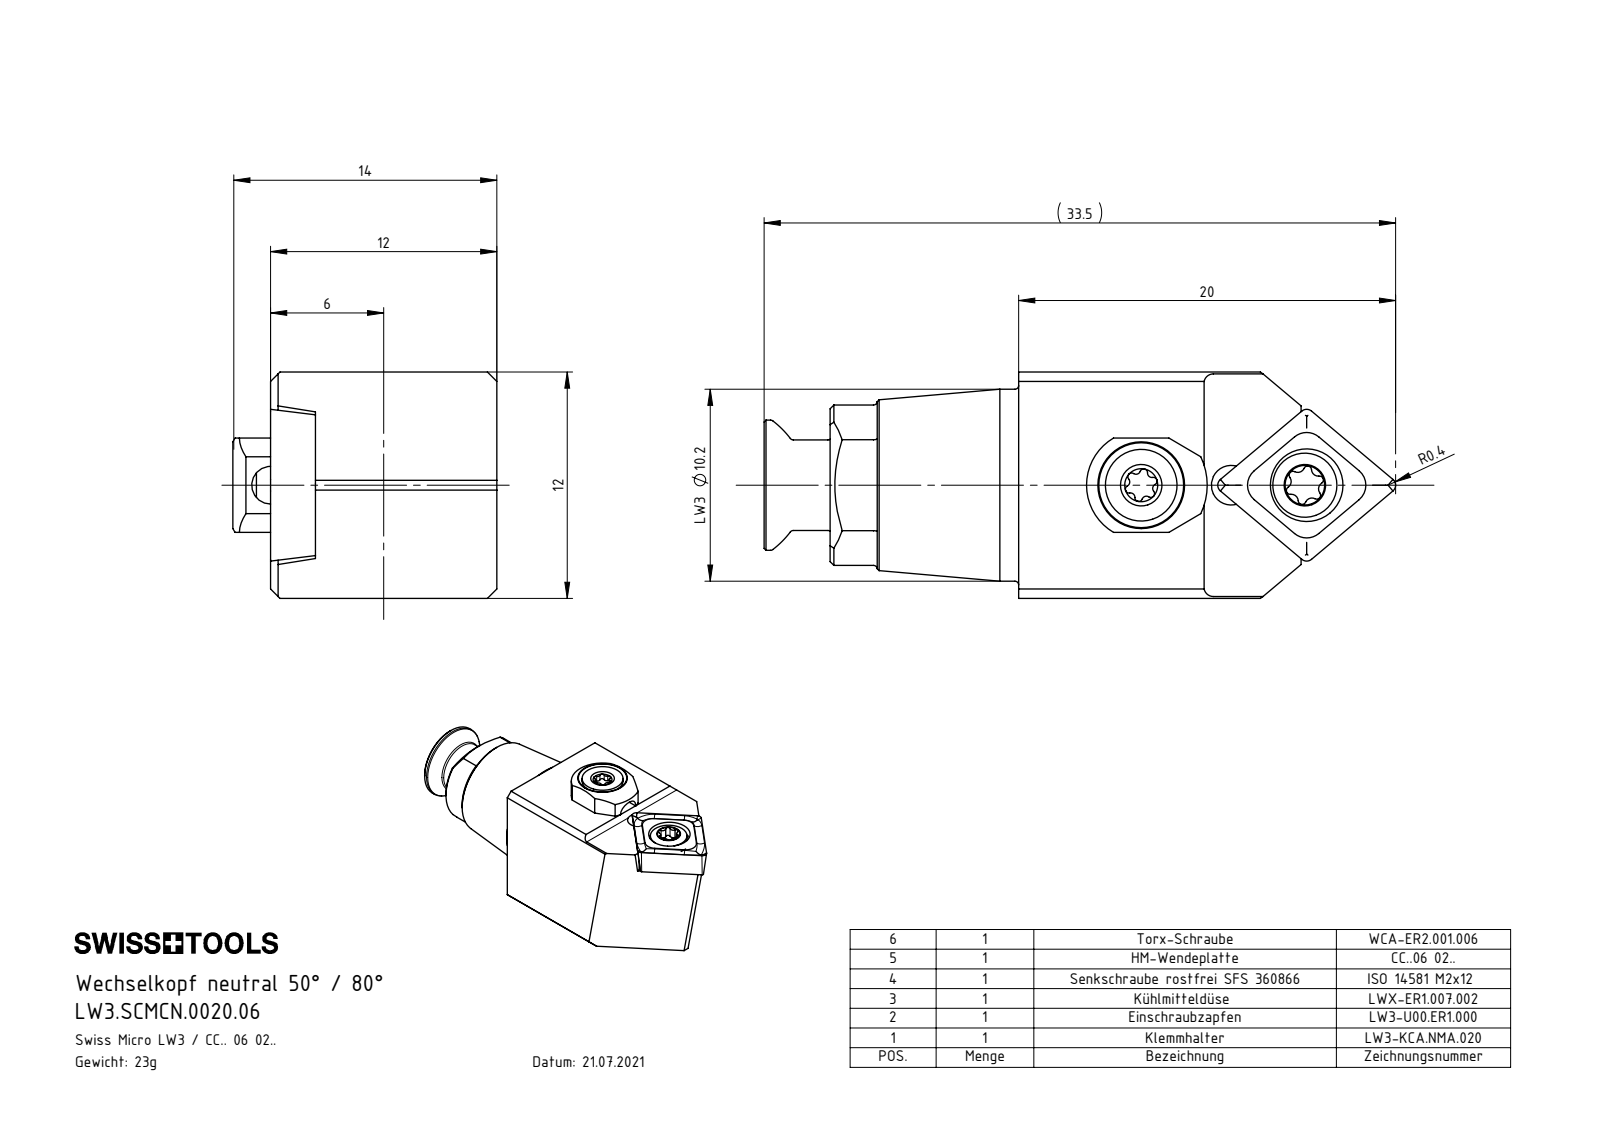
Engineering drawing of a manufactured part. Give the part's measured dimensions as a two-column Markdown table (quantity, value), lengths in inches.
| quantity | value |
| --- | --- |
| part name | LWX-ER1.007.002; ISO 14581 - M2x12; LW3-U00.ER1.000_B; CCMT060204 (+3 more) |
| STEP written by | SolidWorks 2017 (CONFIG_CONTROL_DESIGN) |
| units | inches |
| bodies | 6 solids, 183 faces (67 planar, 51 cylindrical, 65 other) |
| overall size | 1.315 × 0.551 × 0.472 |
| volume | 0.175 in³ |
| surface area | 3.563 in² |
| round holes (diameter × count) | 0.063 × 1, 0.079 × 1, 0.081 × 1, 0.083 × 1, 0.098 × 1, 0.11 × 1, 0.118 × 1, 0.152 × 1, 0.217 × 1 |
| round bosses / shafts (diameter × count) | 0.401 × 1, 0.272 × 1, 0.236 × 1, 0.197 × 1, 0.189 × 1, 0.15 × 1, 0.134 × 1, 0.098 × 1 |
| partial cylindrical surfaces (radius × count) | 0.008 × 8, 0.008 × 6, 0.009 × 6, 0.014 × 4, 0.014 × 2, 0.02 × 1, 0.039 × 1, 0.114 × 1 |
| main face-to-face distances | 0.472, 0.379, 0.094, 0.079, 0.457, 0.078, 0.016, 0.098, 0.528, 0.449 |
| hole center spacings | 0.154, 0.158, 0.188, 0.342, 0.346 |
